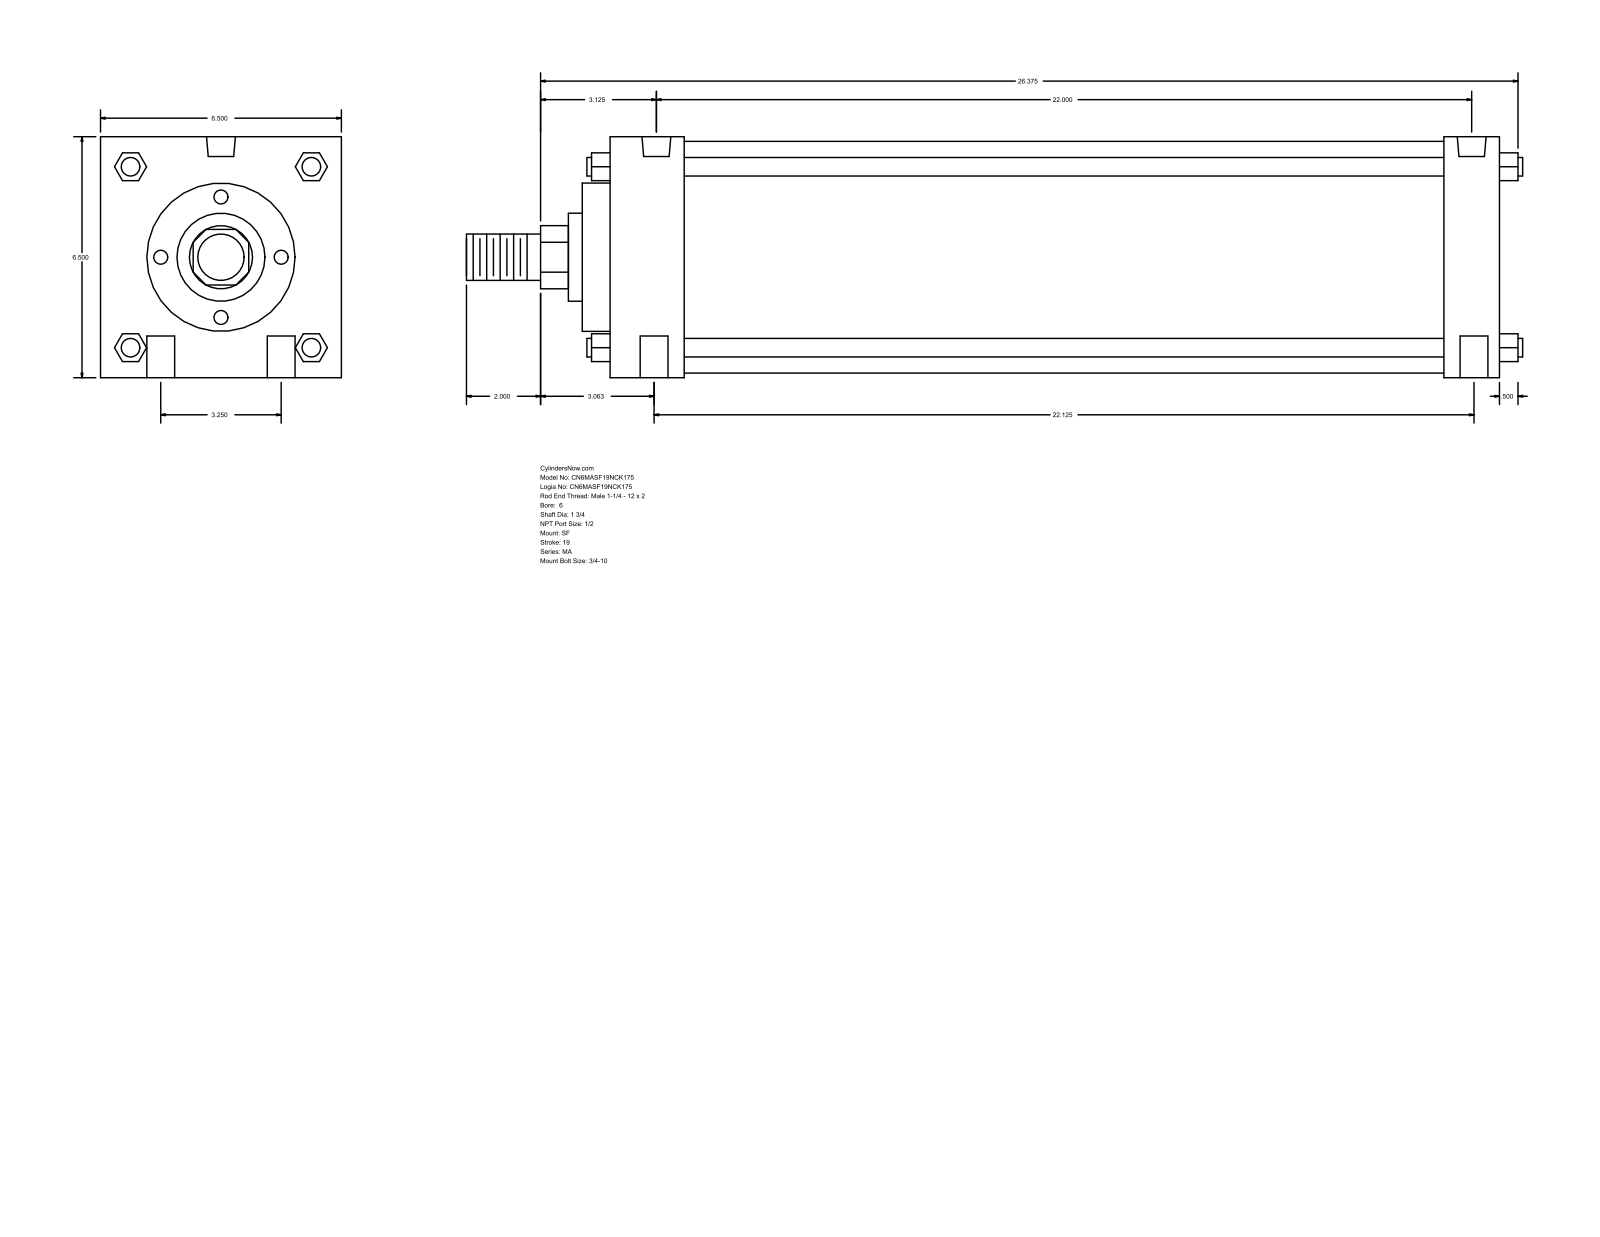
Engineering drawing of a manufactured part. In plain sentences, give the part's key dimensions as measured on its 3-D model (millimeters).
The part is named "MA_SF__0600_1.75". Its 3-D file was written by "GSSL Pune (CONFIG_CONTROL_DESIGN)". It is 0 solids with 126 faces: 95 planar, 31 cylindrical and 0 other. Overall it measures 723.9 by 165.1 by 165.1 millimeters. Round holes: 4 of diameter 19.05, 2 of diameter 17.46, 2 of diameter 19.77. Round bosses or shafts: 4 of diameter 12.7, 1 of diameter 158.75, 1 of diameter 101.6, 1 of diameter 60.33, 1 of diameter 44.45, 1 of diameter 31.75. Partial cylindrical surfaces (rounded edges, fillets, slot ends): 1 of radius 21.63. The main face-to-face distances are 165.1, 609.61, 19.05, 50.8, 571.5, 38.11, 520.7, 558.81, 69.85, 590.55. The hole center spacings are 41.3, 561.9, 82.54, 558.79, 561.97, 568.
